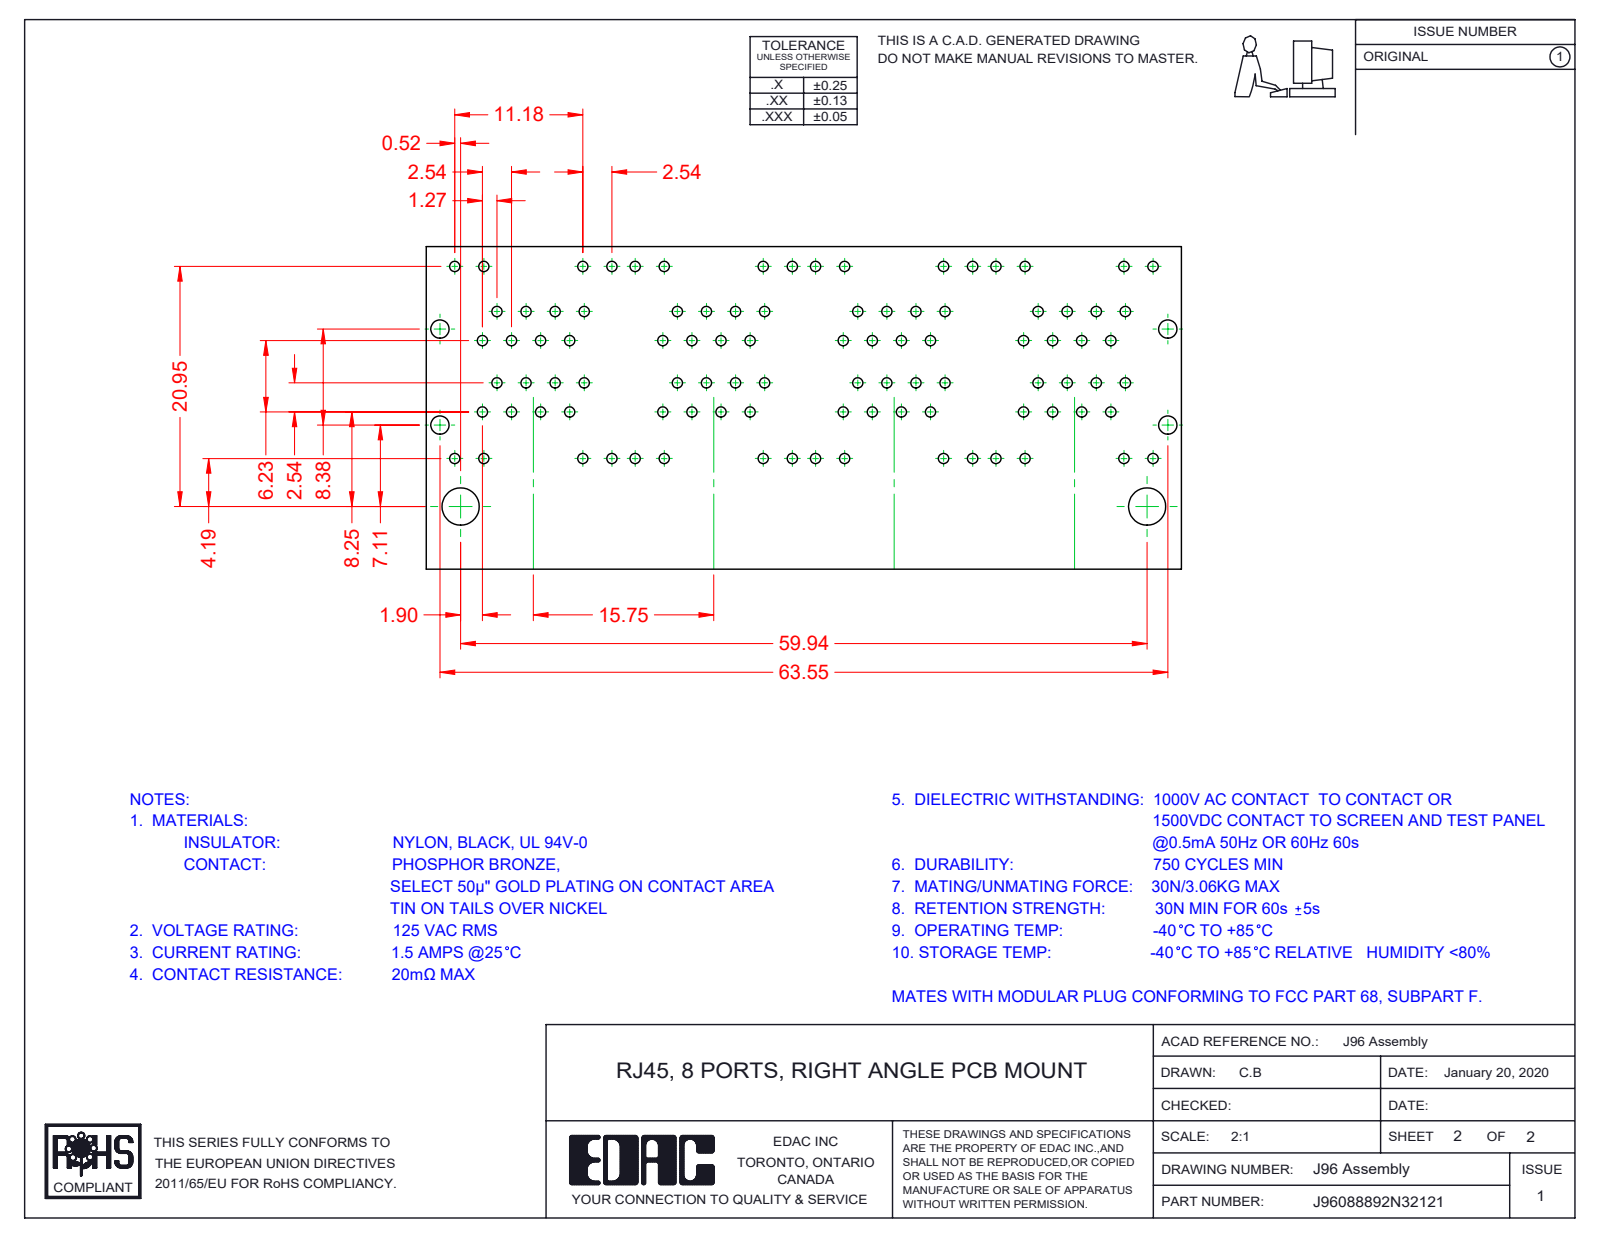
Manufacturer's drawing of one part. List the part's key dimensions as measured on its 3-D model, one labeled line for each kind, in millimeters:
Part name (STEP PRODUCT): 96 Contacts Lower; J96088892N32121; 96 LED RH Upper_2-Red; 96 Insulator Insert (+8 more)
STEP written by: SolidWorks 2016 (CONFIG_CONTROL_DESIGN)
Units: millimetres
Bodies: 96 solids, 7642 faces (6069 planar, 1307 cylindrical, 266 other)
Overall size (bounding box): 64.05 × 29.58 × 28.68
Volume: 24 160 mm³ · Surface area: 63 658 mm²
Round holes (diameter × count): ⌀1.7 ×3
Round bosses / shafts (diameter × count): ⌀1.68 ×3
Partial cylindrical surfaces — rounded edges, fillets, slot ends (radius × count): R0.25 ×124, R0.35 ×73, R1 ×72, R0.5 ×49, R0.91 ×32, R0.2 ×21, R0.7 ×11, R0.22 ×8
Main face-to-face distances: 15.75, 0.35, 9.95, 1.17, 1.6, 0.54, 9.98, 10.18, 12.67, 3.37
Hole centre spacings: 15.75, 31.5
